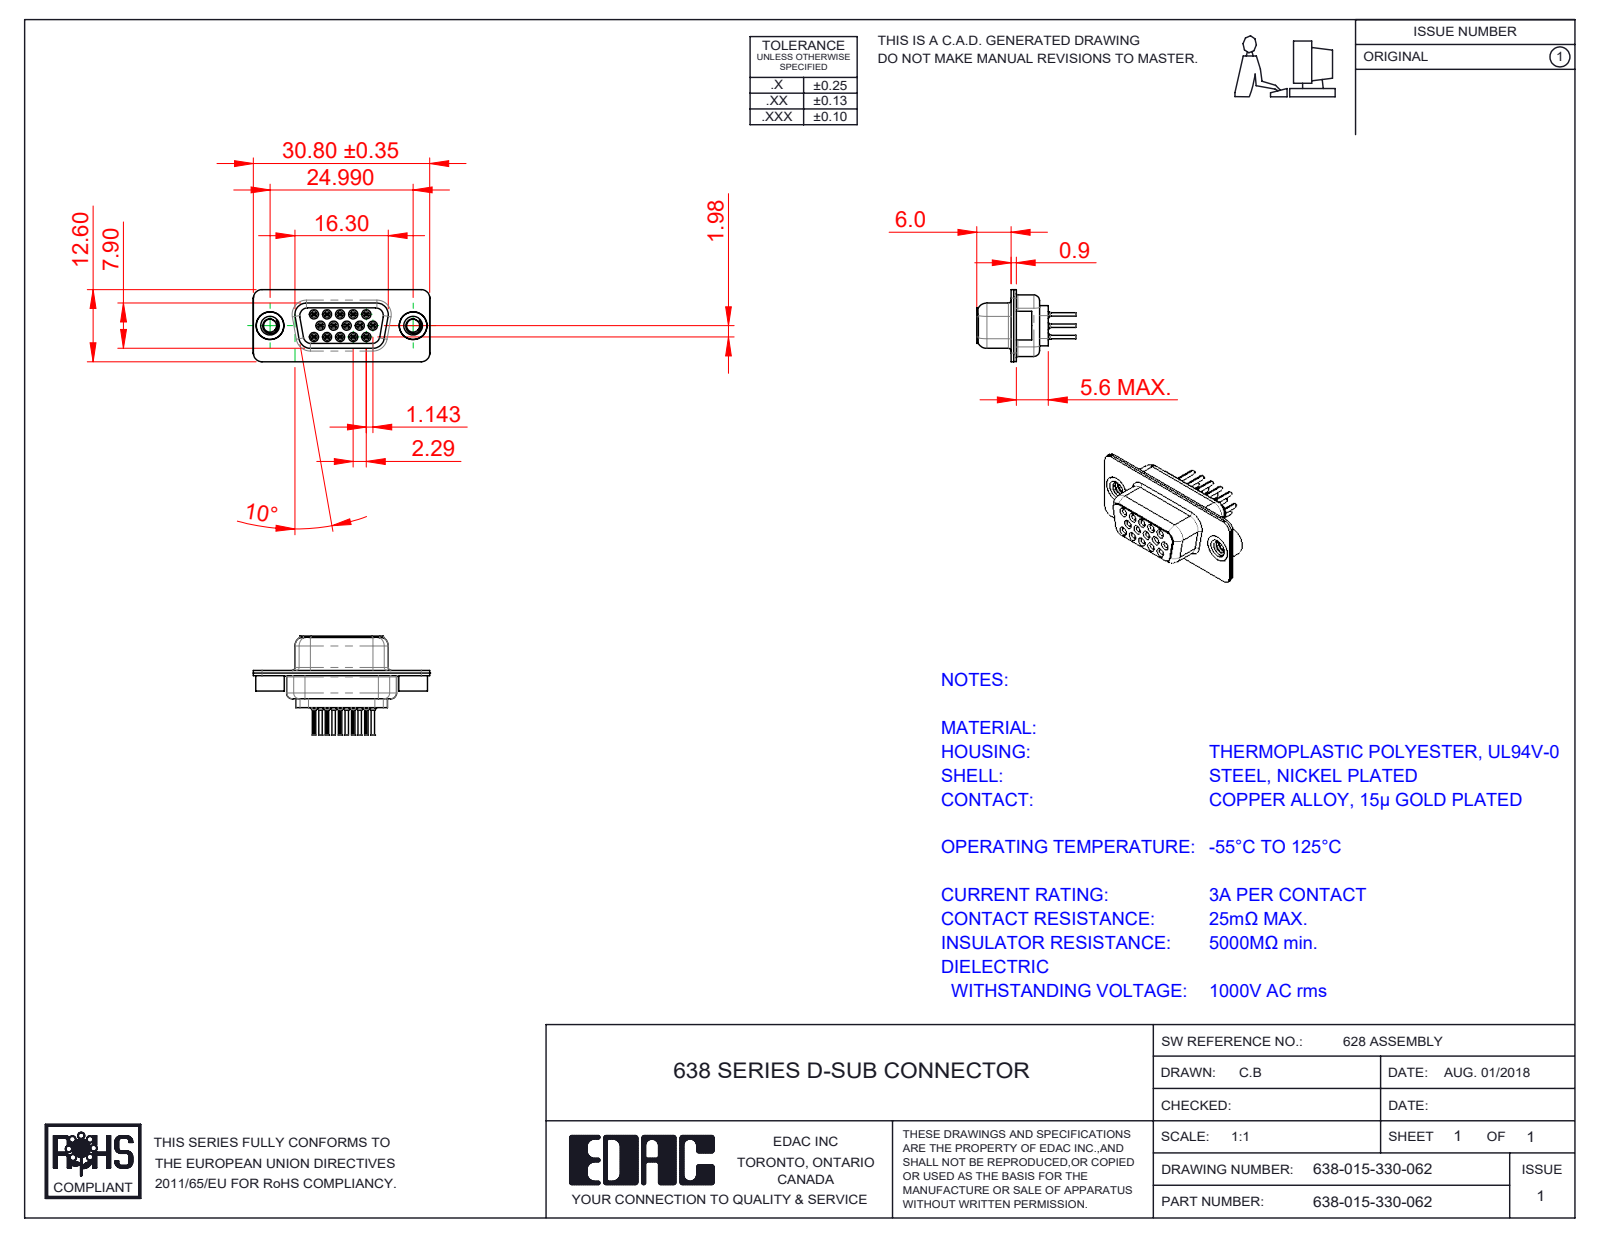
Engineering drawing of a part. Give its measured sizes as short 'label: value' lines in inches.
name: 638 Shell Rear_15 Contacts; 638 Housing_15 Contacts; 638-015-330-062; 638 Shell Front_15 Contacts (+4 more)
written by: SolidWorks 2020 (CONFIG_CONTROL_DESIGN)
unit: in
bodies: 20 solids, 2184 faces (532 planar, 632 cylindrical, 1020 other)
size: 1.213 × 0.681 × 0.496
volume: 0.096 in³; area: 8.677 in²
holes: 15× ⌀0.008, 15× ⌀0.031, 15× ⌀0.039, 15× ⌀0.043, 15× ⌀0.063, 15× ⌀0.067, 15× ⌀0.071, 2× ⌀0.079, 2× ⌀0.089, 2× ⌀0.157, 2× ⌀0.159, 2× ⌀0.191
bosses: 15× ⌀0.079, 15× ⌀0.059, 15× ⌀0.047, 15× ⌀0.024, 2× ⌀0.197, 2× ⌀0.195, 2× ⌀0.189
rounds: 30× R0.004, 20× R0.059, 12× R0.079, 10× R0.011, 8× R0.061, 5× R0.053, 4× R0.01, 4× R0.02
face distances: 0.018, 0.035, 0.016, 0.056, 0.35, 0.26, 0.055, 0.09, 0.033, 0.278
hole spacings: 0.156, 0.09, 0.18, 0.09, 0.238, 0.238, 0.27, 0.312
